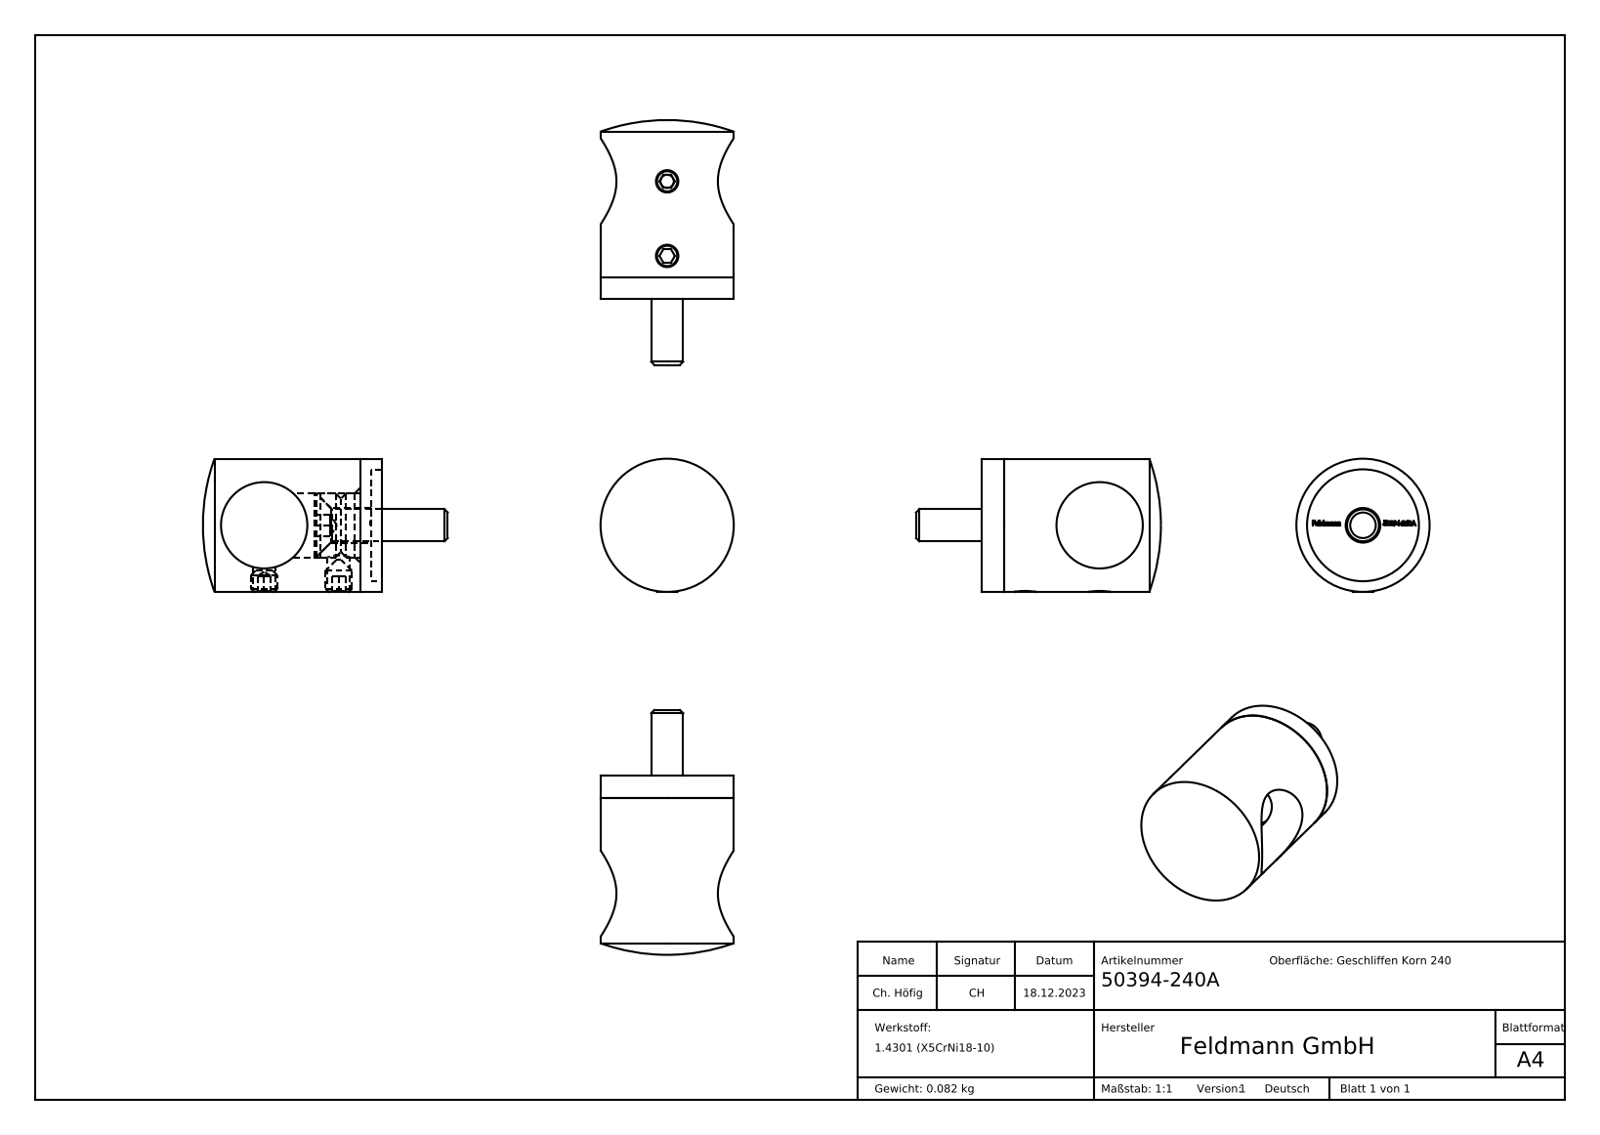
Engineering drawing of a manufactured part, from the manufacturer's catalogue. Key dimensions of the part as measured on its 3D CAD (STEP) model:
Part name (STEP PRODUCT): 50394-240A; 5039X-240A Konfig Teil1; 5039X-240A Konfig Teil2_50394-240A Teil2; DIN913_DIN 913 M5x4 (+7 more)
STEP written by: SolidWorks 2018 (CONFIG_CONTROL_DESIGN)
Units: millimetres
Bodies: 5 solids, 339 faces (182 planar, 28 cylindrical, 129 other)
Overall size (bounding box): 70 × 45.95 × 25
Volume: 10 383 mm³ · Surface area: 6 908 mm²
Round holes (diameter × count): ⌀4.2 ×2, ⌀6.5 ×1, ⌀16.2 ×1, ⌀21 ×1
Round bosses / shafts (diameter × count): ⌀5 ×2, ⌀25 ×1, ⌀12 ×1, ⌀6 ×1
Main face-to-face distances: 2, 2.1, 4.1, 12.65, 10.55, 8.55, 9.5, 7.5, 4, 1.05
Hole centre spacings: 14
